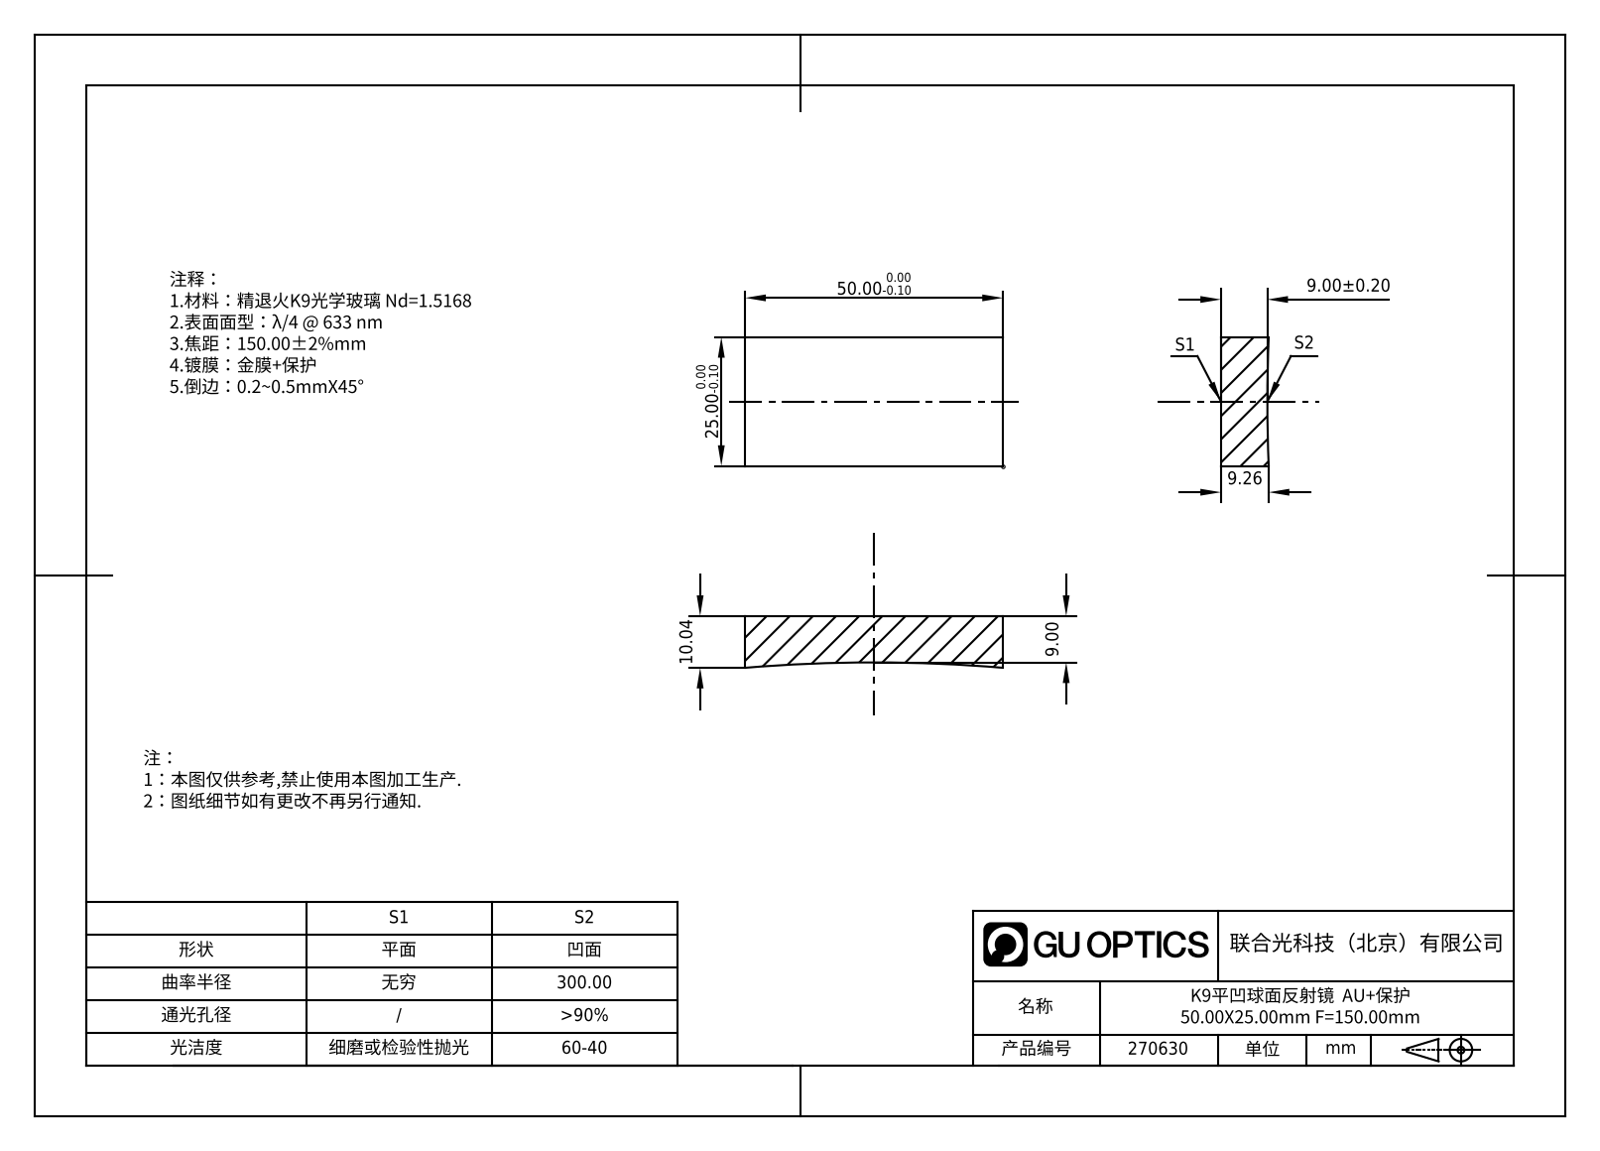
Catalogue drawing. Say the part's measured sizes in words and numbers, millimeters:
The part is named "GM13-50x25-150". Its 3-D file was written by "SolidWorks 2022 (AUTOMOTIVE_DESIGN)". It is 1 solid with 7 faces: 5 planar, 0 cylindrical and 2 other. Overall it measures 50 by 25 by 10.3 millimeters. Its volume is 11 793 cubic millimeters and its surface area 3 969 square millimeters. The main face-to-face distances are 25, 50.
